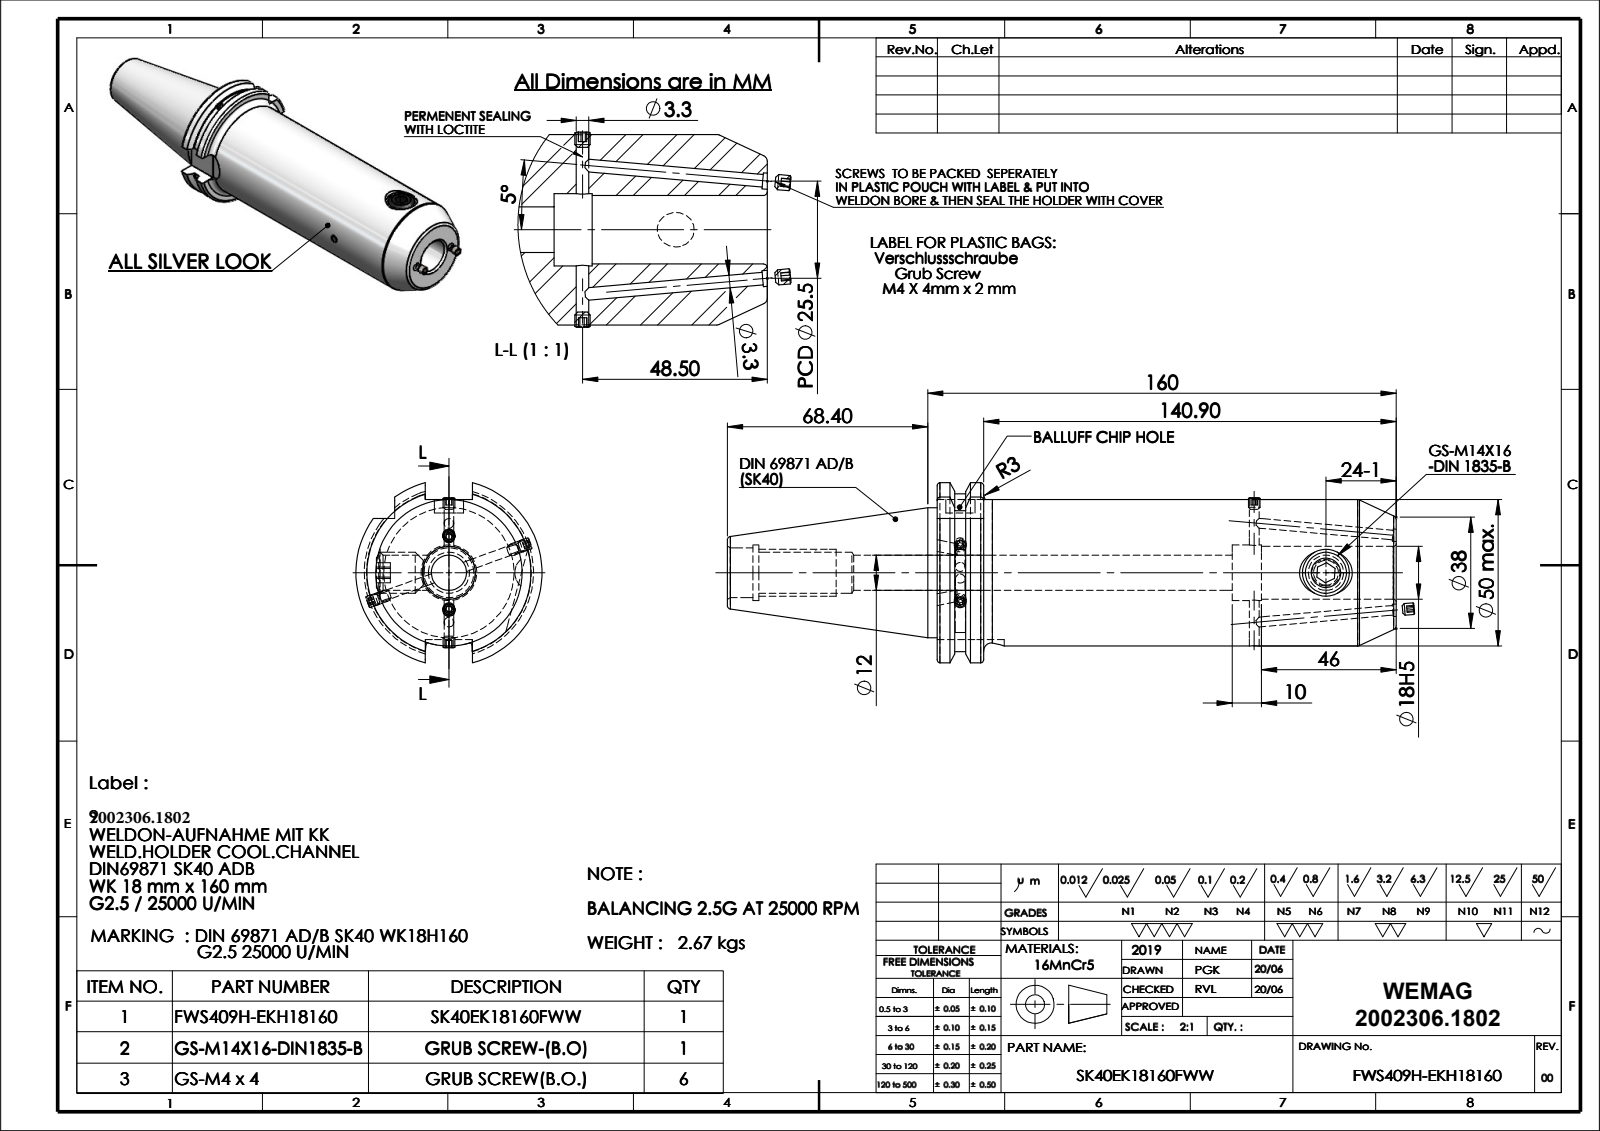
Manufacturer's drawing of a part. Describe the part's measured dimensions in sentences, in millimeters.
The part is named "91406-WK218160". Its 3-D file was written by "SolidWorks 2018 (CONFIG_CONTROL_DESIGN)". It is 2 solids with 139 faces: 40 planar, 55 cylindrical and 44 other. Overall it measures 228.4 by 63.55 by 61.48 millimeters. Its volume is 343 967 cubic millimeters and its surface area 54 708 square millimeters. Round holes: 4 of diameter 3.3, 2 of diameter 4.2, 2 of diameter 12, 1 of diameter 10, 1 of diameter 14, 1 of diameter 16, 1 of diameter 17, 1 of diameter 18, 1 of diameter 19. Round bosses or shafts: 1 of diameter 50, 1 of diameter 44.45. Partial cylindrical surfaces (rounded edges, fillets, slot ends): 2 of radius 8.05, 1 of radius 28.12, 1 of radius 31.77. The main face-to-face distances are 15.9, 156.8, 140.9, 47.8, 16.1, 100.8, 84.9, 56, 71.6, 87.5. The hole center spacings are 100.35.
